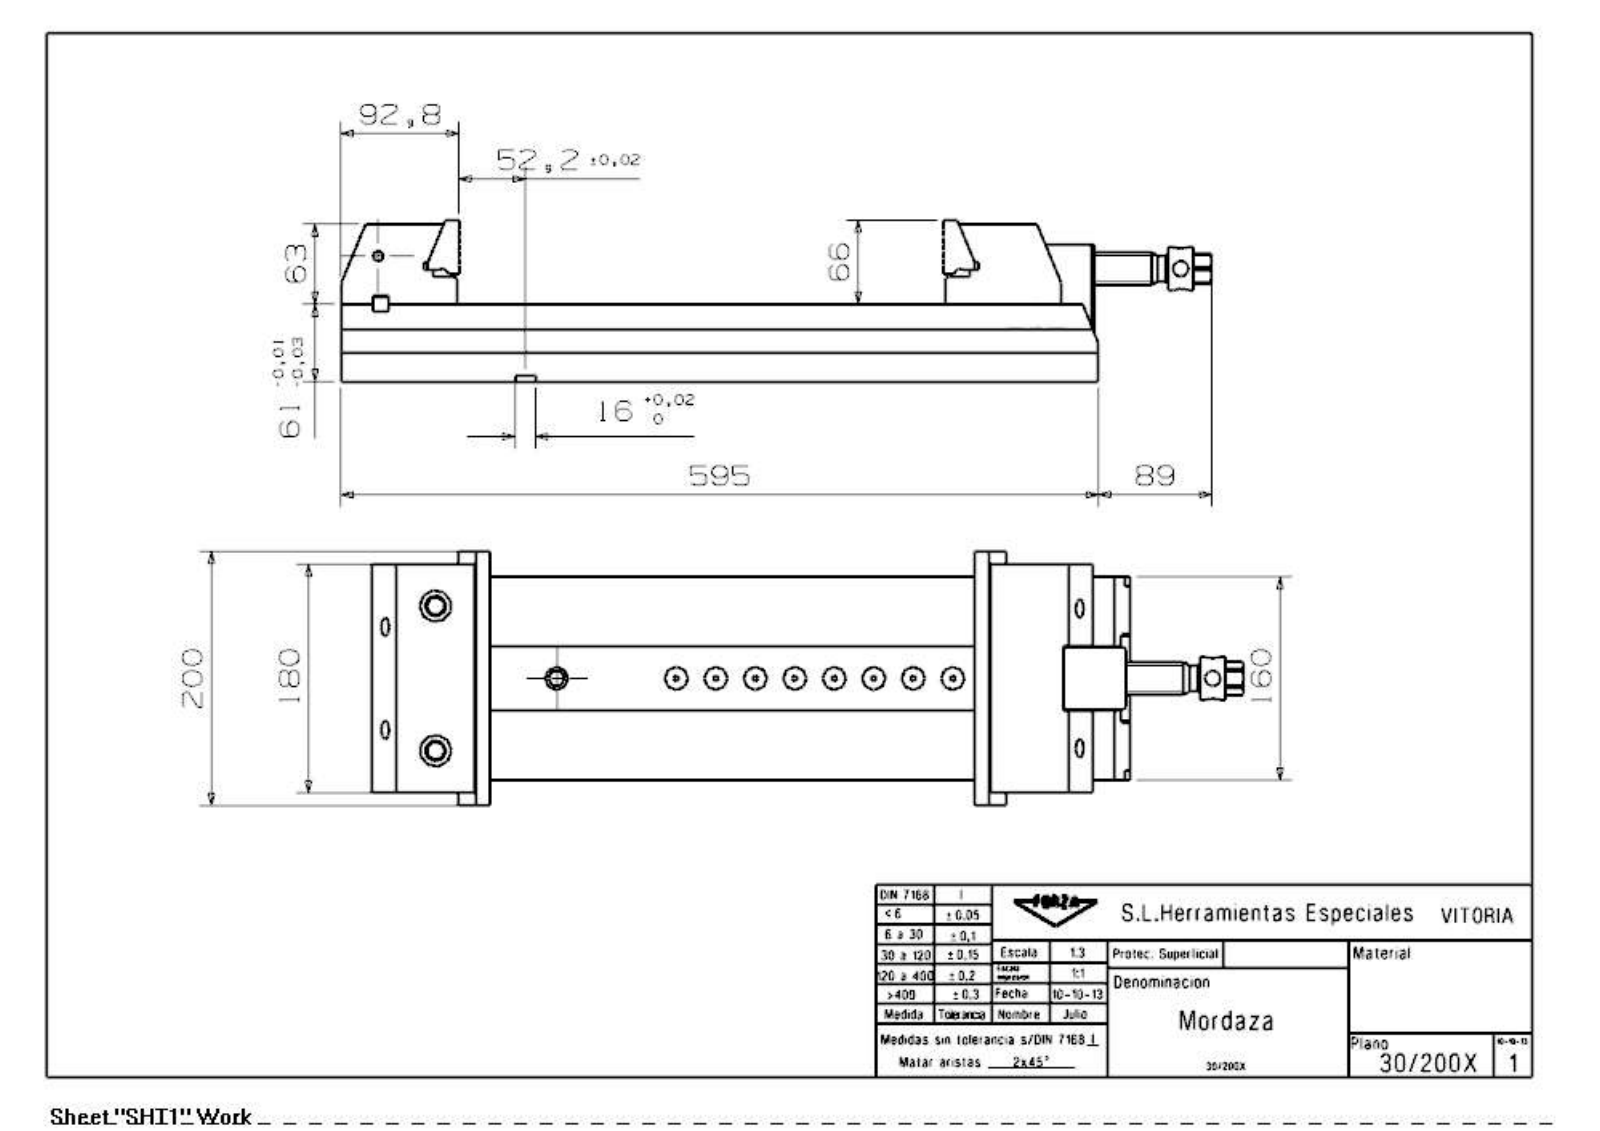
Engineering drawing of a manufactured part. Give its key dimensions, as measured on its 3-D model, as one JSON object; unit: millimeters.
{"part_name": "30_200X_Mordaza", "step_written_by": "SIEMENS PLM Software NX 7.5 (CONFIG_CONTROL_DESIGN)", "units": "millimeters", "bodies": {"solids": 12, "faces": 489, "planar": 277, "cylindrical": 147, "other": 65}, "overall_size": [684, 200, 126.95], "volume_mm3": 6434000, "surface_area_mm2": 668824, "round_holes": [[5, 11], [15, 6], [5.19, 5], [13, 5], [6.99, 4], [8.5, 4], [10, 4], [8.78, 3], [10.58, 3], [19, 3], [12, 2], [12.38, 2]], "round_bosses_or_shafts": [[34, 1], [33.8, 1], [26, 1], [20, 1], [16.5, 1]], "partial_cylinders_radius": [[0.4, 24], [1.5, 4], [8, 4], [20, 4], [1.6, 2], [6, 2], [7, 2], [4, 1]], "face_to_face_distances": [61, 31.8, 29.2, 7.5, 27.2, 59, 160, 2, 63, 152.5], "hole_center_spacings": [31, 62, 93, 14.5, 95.5, 124, 155, 186]}
